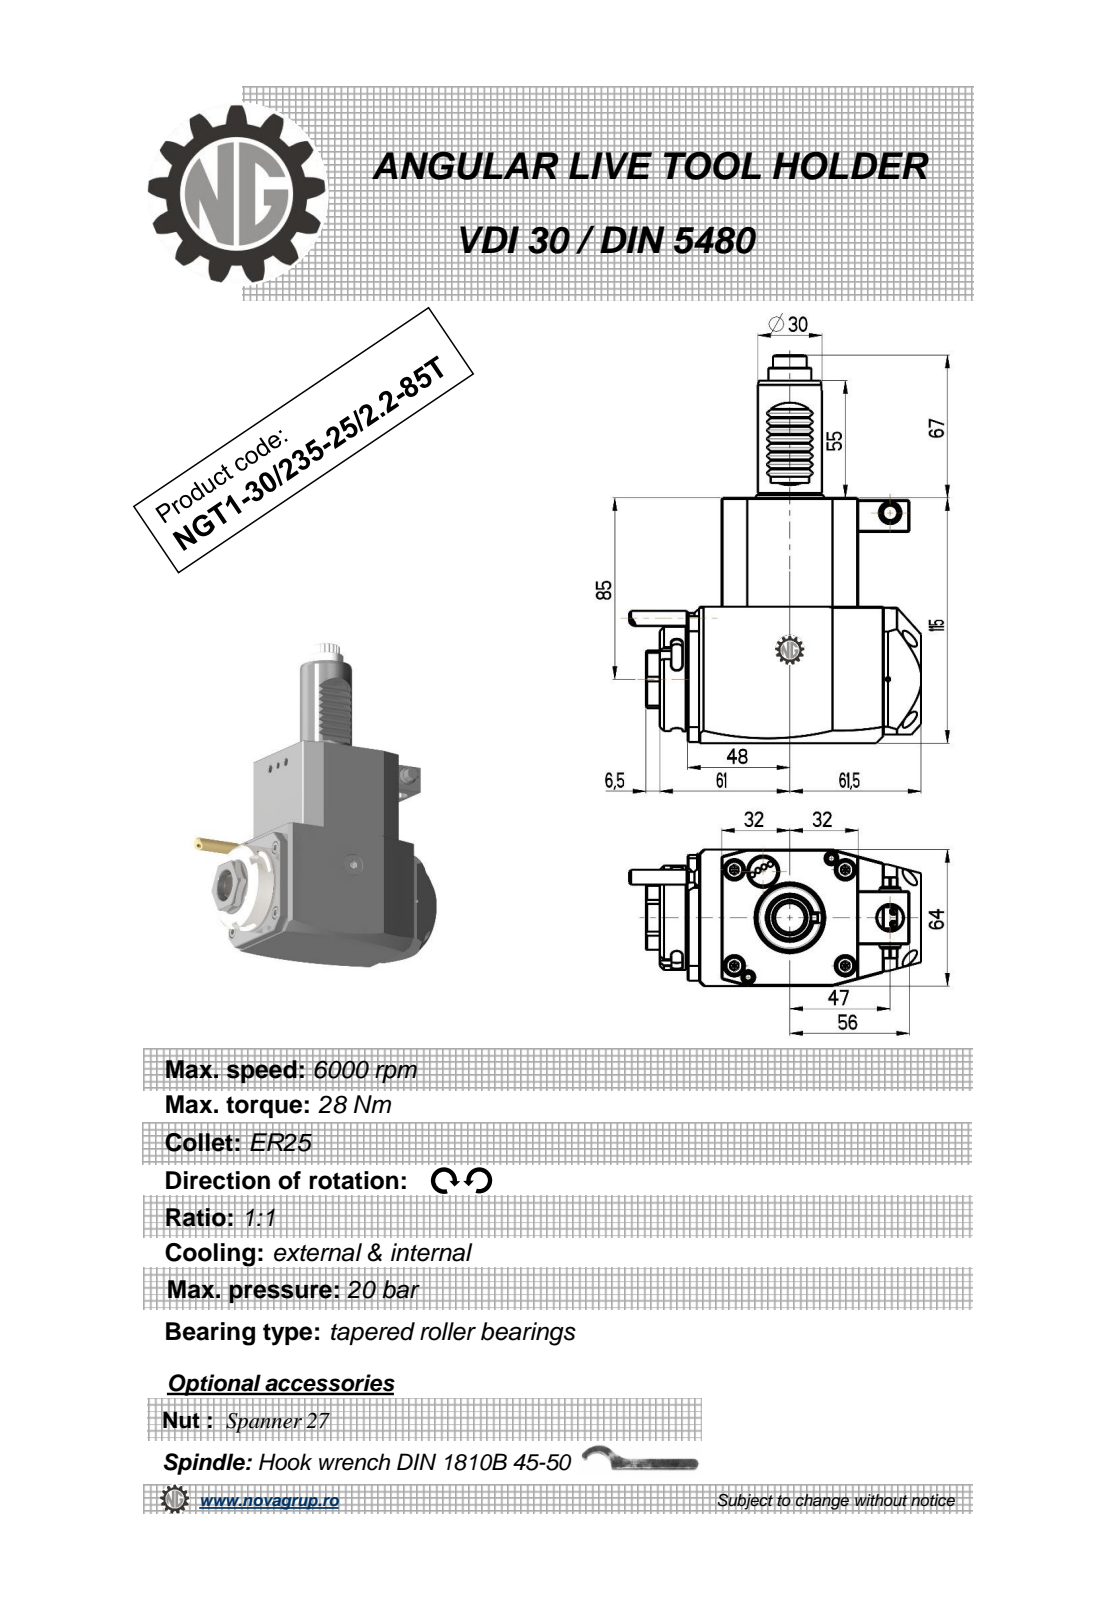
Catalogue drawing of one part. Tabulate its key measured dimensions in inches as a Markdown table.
| quantity | value |
| --- | --- |
| part name | NGT1_30_235_25_1_2_85T |
| STEP written by | PRO/ENGINEER BY PARAMETRIC TECHNOLOGY CORPORATION, 2010280 (CONFIG_CONTROL_DESIGN) |
| units | inches |
| bodies | 1 solid, 461 faces (211 planar, 162 cylindrical, 88 other) |
| overall size | 7.165 × 5.389 × 2.52 |
| volume | 41.51 in³ |
| surface area | 90.3 in² |
| round holes (diameter × count) | 0.098 × 1, 0.118 × 1, 0.374 × 1, 0.472 × 1, 0.709 × 1 |
| round bosses / shafts (diameter × count) | 0.315 × 2, 1.929 × 1, 1.654 × 1, 1.181 × 1, 0.787 × 1, 0.394 × 1, 0.276 × 1, 0.197 × 1 |
| partial cylindrical surfaces (radius × count) | 0.078 × 36, 0.012 × 8, 0.098 × 6, 7.087 × 2, 0.152 × 1, 0.167 × 1, 0.177 × 1, 0.279 × 1 |
| main face-to-face distances | 2.52, 4.528, 0.63, 3.15, 2.008, 1.161, 0.512, 4.823, 4.311, 3.681 |
| hole center spacings | 1.348, 2.032, 3.012 |
